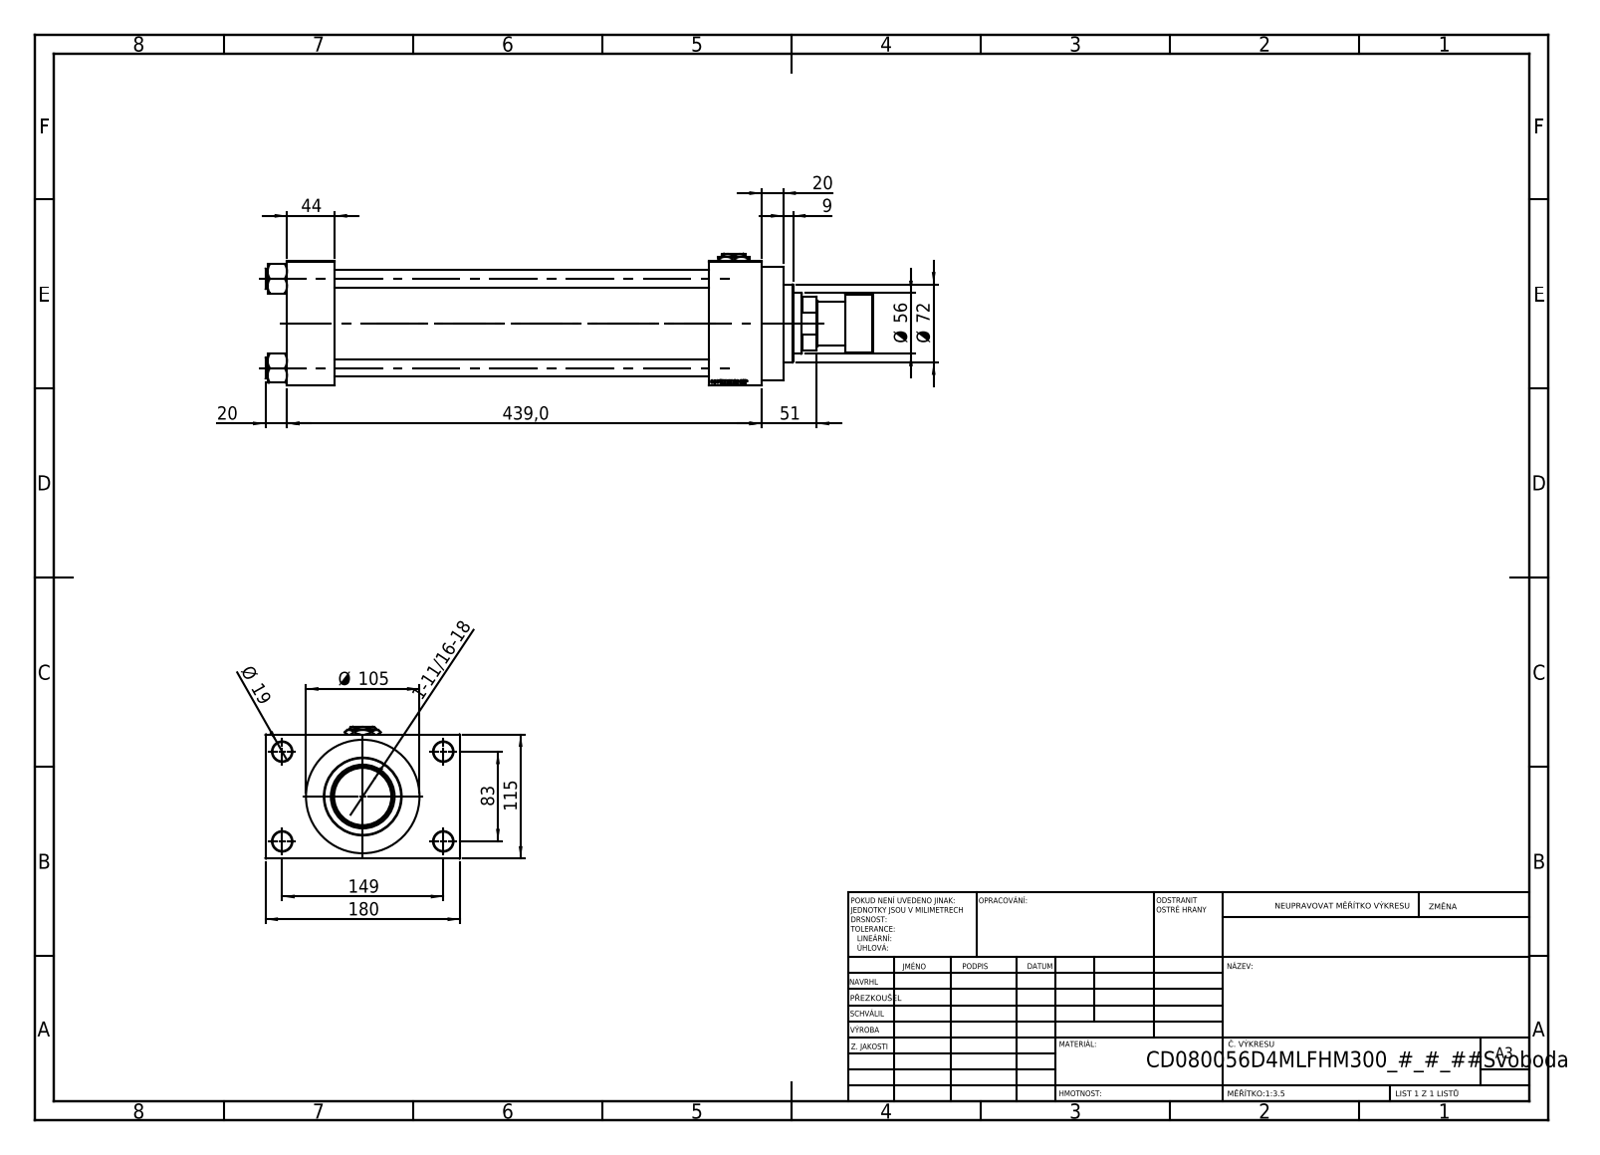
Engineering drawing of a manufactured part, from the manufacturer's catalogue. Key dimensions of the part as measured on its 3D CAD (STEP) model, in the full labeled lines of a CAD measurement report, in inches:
Part name (STEP PRODUCT): V215CD_VC_A; V215CD_NUT_M5_D; V215CD_D_Body; V215CR_ROD_END_F (+3 more)
STEP written by: SolidWorks 2019 (CONFIG_CONTROL_DESIGN)
Units: inches
Bodies: 13 solids, 1205 faces (570 planar, 91 cylindrical, 544 other)
Overall size (bounding box): 22.126 × 7.087 × 4.803
Volume: 204.4 in³ · Surface area: 890 in²
Round holes (diameter × count): ⌀0.63 ×4, ⌀0.709 ×4, ⌀0.276 ×2, ⌀1.041 ×2, ⌀1.378 ×2, ⌀1.594 ×1, ⌀2.205 ×1, ⌀2.323 ×1, ⌀2.402 ×1, ⌀2.835 ×1, ⌀3.15 ×1
Round bosses / shafts (diameter × count): ⌀0.748 ×4, ⌀4.134 ×1, ⌀3.386 ×1, ⌀2.126 ×1, ⌀1.575 ×1
Main face-to-face distances: 4.528, 13.622, 1.732, 15.354, 1.28, 17.283, 15.551, 1.929, 5.807, 7.087
Hole centre spacings: 1.305, 2.302, 3.256, 3.357, 3.513, 4.561, 5.607, 3.268
